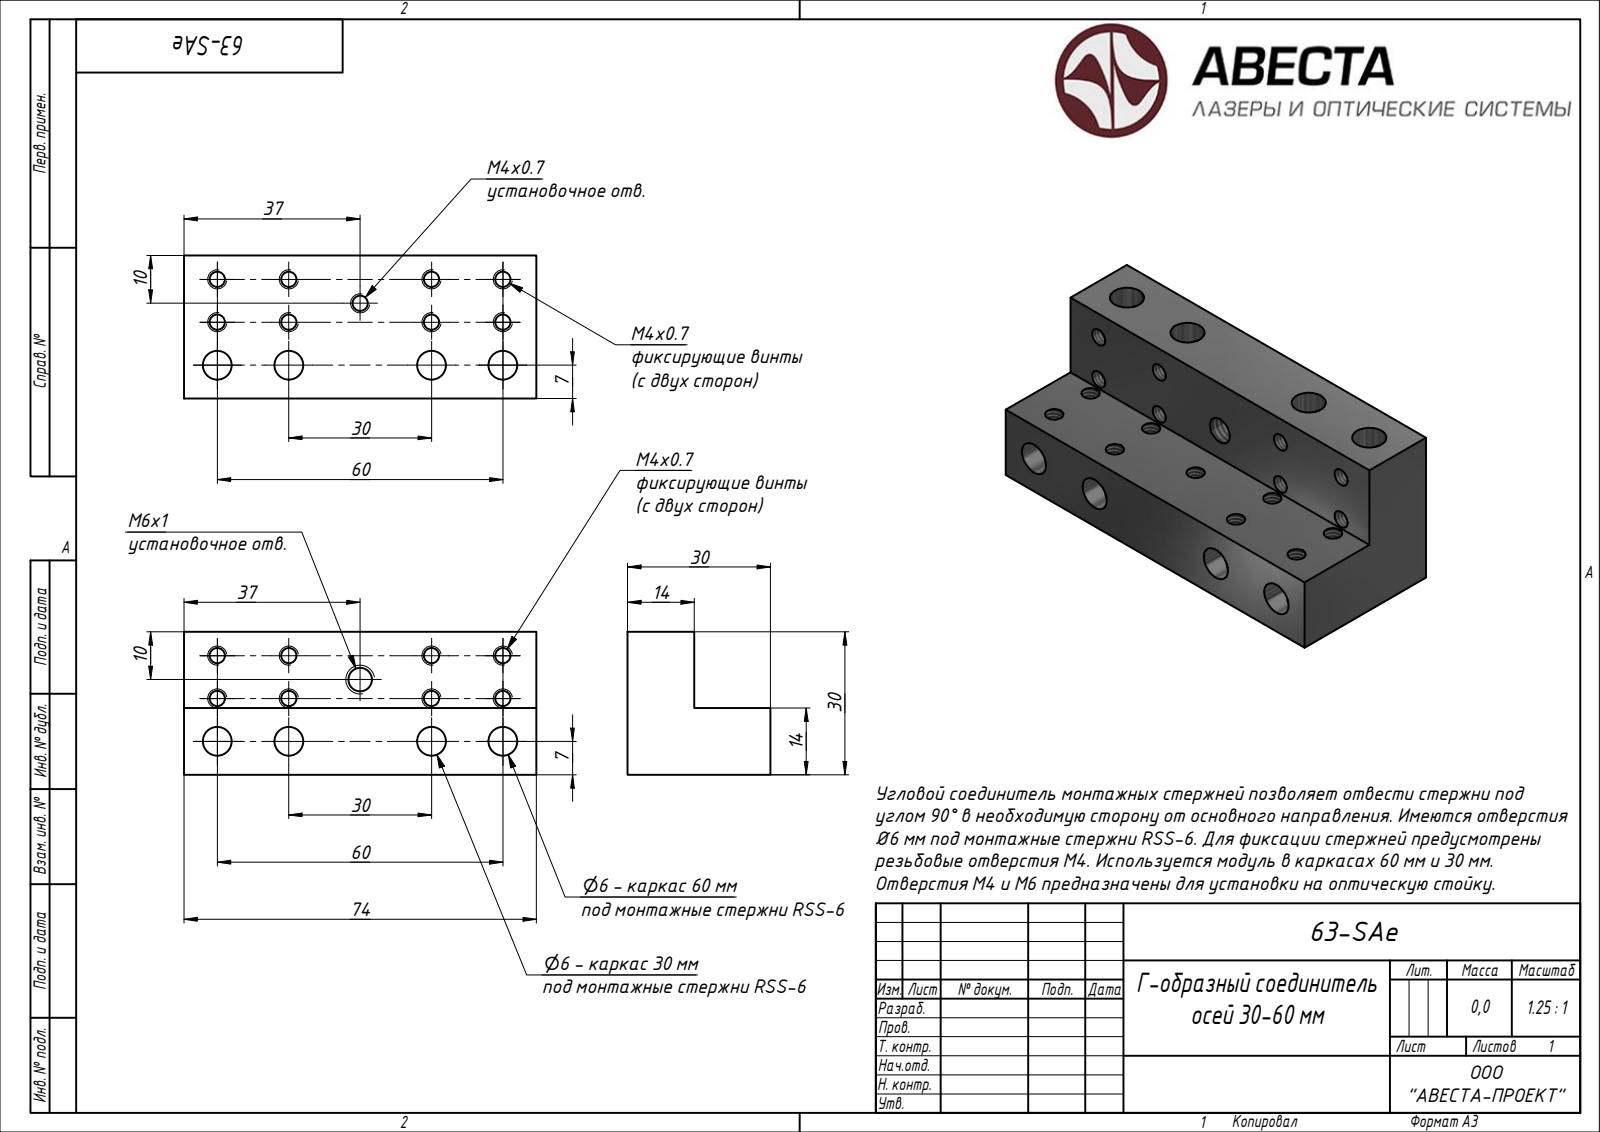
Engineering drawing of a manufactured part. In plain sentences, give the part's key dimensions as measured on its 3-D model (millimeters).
Its 3-D file was written by "Rhino 7.34 (AUTOMOTIVE_DESIGN)". It is 1 solid with 108 faces: 8 planar, 100 cylindrical and 0 other. Overall it measures 74 by 30 by 30 millimeters. Its volume is 39 978 cubic millimeters and its surface area 14 808 square millimeters. Round holes: 17 of diameter 3.24, 8 of diameter 6, 1 of diameter 4.92. The main face-to-face distances are 14, 30, 16, 74. The hole center spacings are 9, 17.49, 45.89, 15, 45, 18, 23.43, 31.32.
